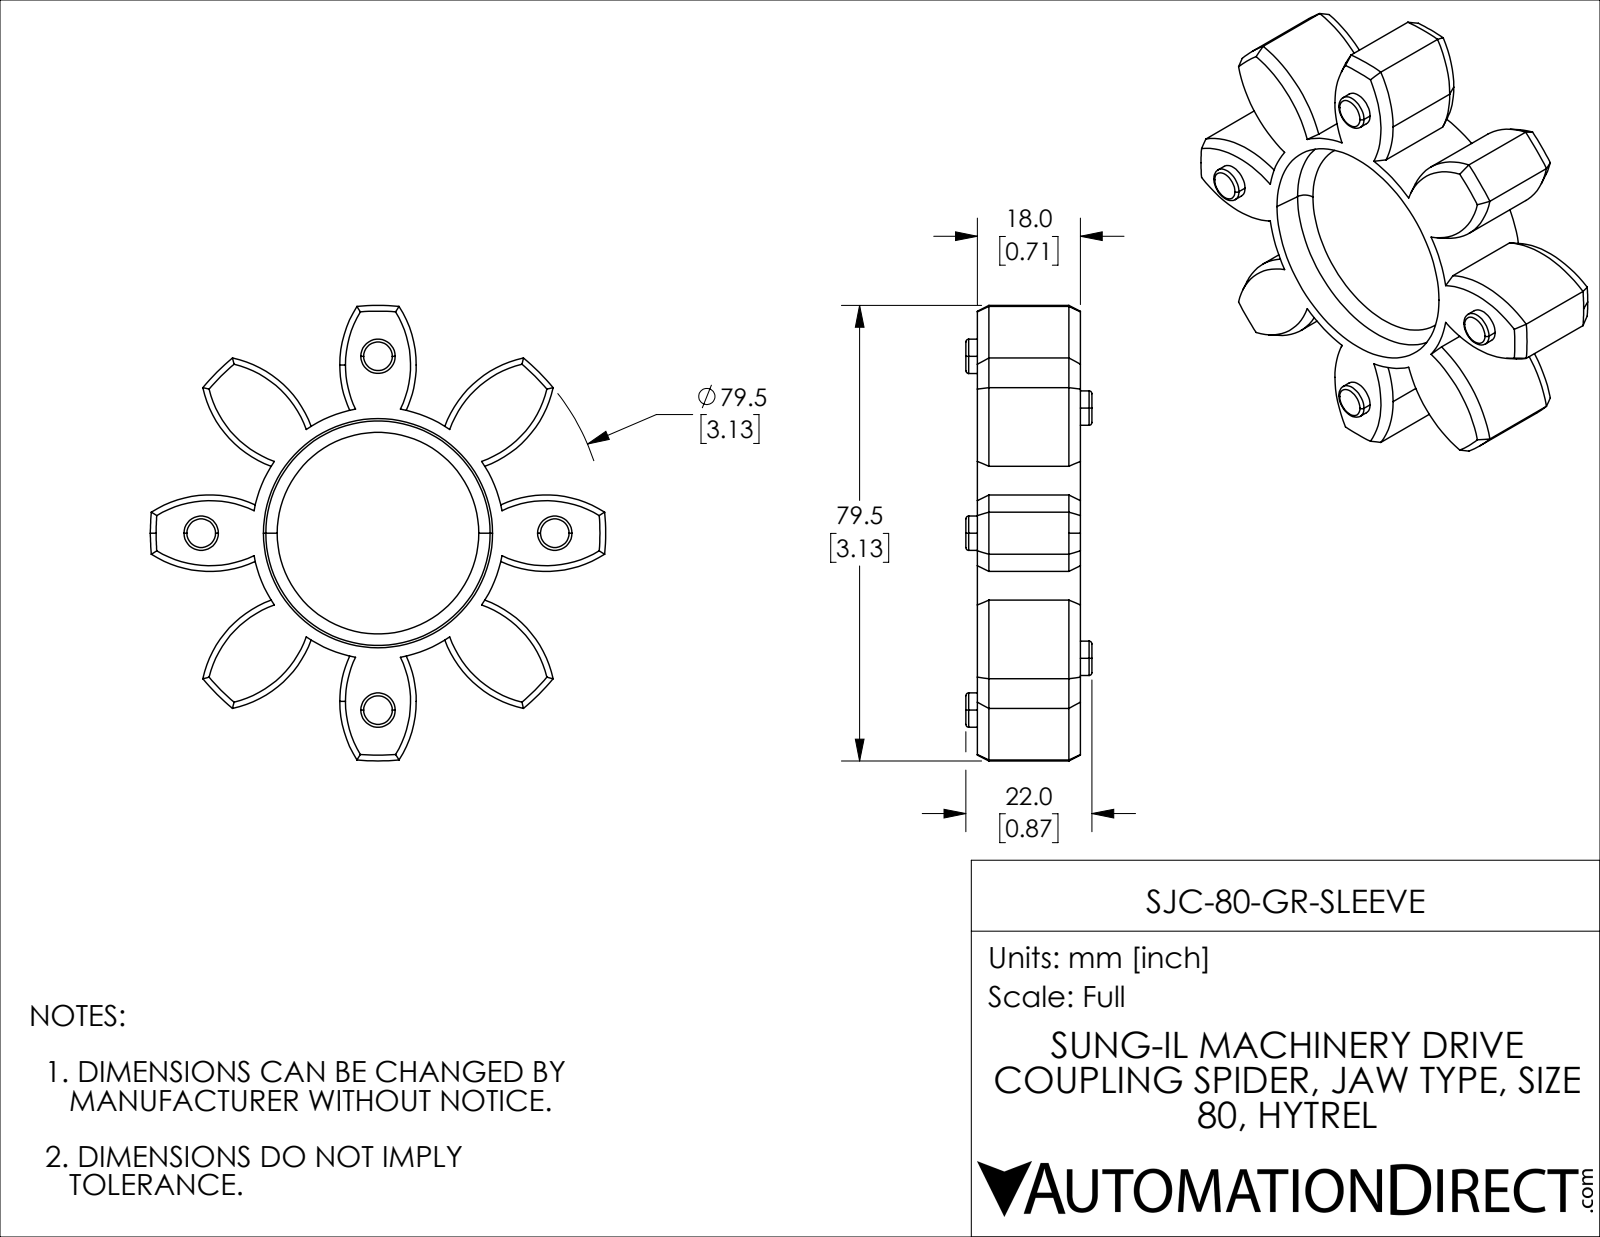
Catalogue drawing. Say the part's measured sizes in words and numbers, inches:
The part is named "SJC-80-GR-SLEEVE". Its 3-D file was written by "SolidWorks 2021 (CONFIG_CONTROL_DESIGN)". It is 1 solid with 141 faces: 12 planar, 51 cylindrical and 78 other. Overall it measures 3.13 by 3.13 by 0.866 inches. Its volume is 2.547 cubic inches and its surface area 23.25 square inches. Round bosses or shafts: 8 of diameter 0.236. Partial cylindrical surfaces (rounded edges, fillets, slot ends): 8 of radius 0.742, 1 of radius 0.866, 1 of radius 1.565. The main face-to-face distances are 0.256, 0.453, 0.709, 0.197, 0.079, 0.335, 0.531, 0.787, 0.866.
